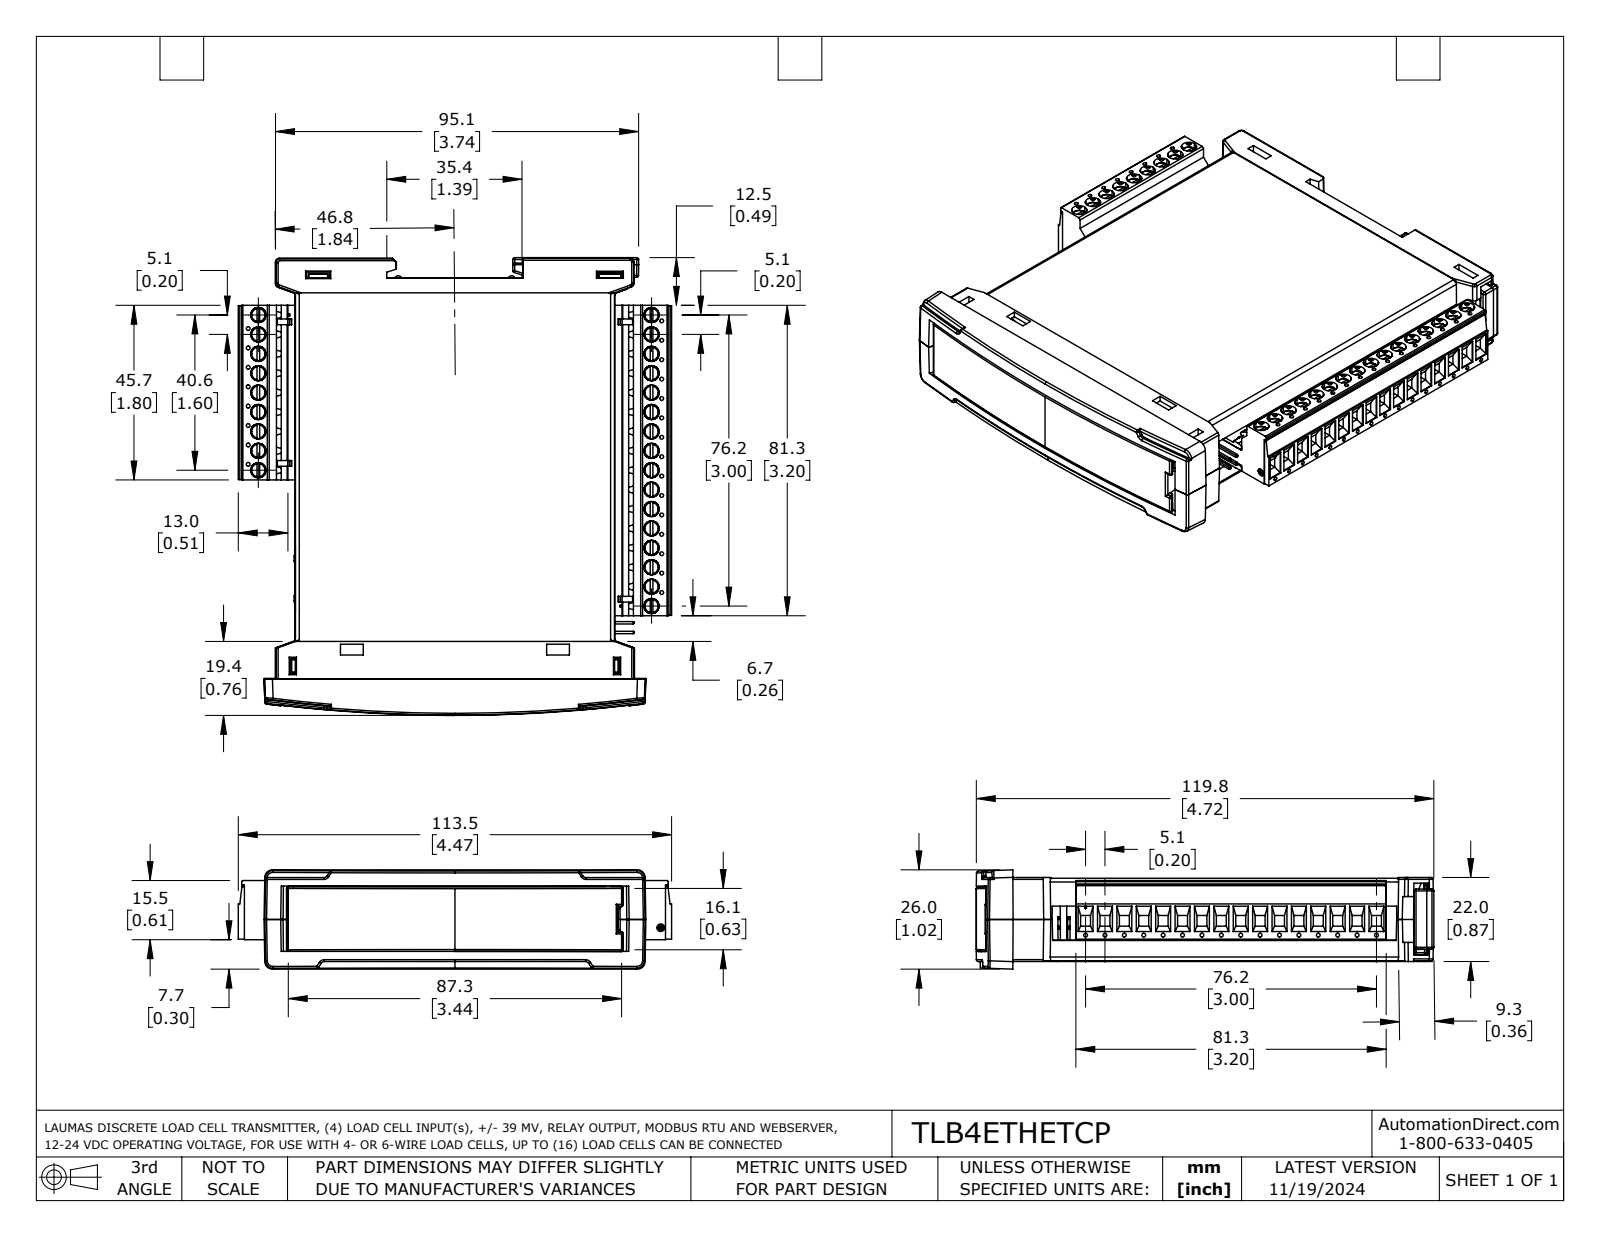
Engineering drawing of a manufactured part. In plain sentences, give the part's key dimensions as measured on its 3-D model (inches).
The part is named "TLB4ETHETCP". Its 3-D file was written by "SolidWorks 2021 (AUTOMOTIVE_DESIGN)". It is 26 solids with 6312 faces: 4003 planar, 1674 cylindrical and 635 other. Overall it measures 4.719 by 4.469 by 1.023 inches. Its volume is 5.296 cubic inches and its surface area 172.4 square inches. Round holes: 56 of diameter 0.039, 25 of diameter 0.157, 16 of diameter 0.059, 16 of diameter 0.146, 6 of diameter 0.079, 4 of diameter 0.029, 4 of diameter 0.035, 2 of diameter 0.067. Round bosses or shafts: 25 of diameter 0.152, 25 of diameter 0.055, 16 of diameter 0.108, 4 of diameter 0.114, 2 of diameter 0.06, 2 of diameter 0.051, 1 of diameter 0.093. Partial cylindrical surfaces (rounded edges, fillets, slot ends): 157 of radius 0.02, 109 of radius 0.004, 64 of radius 0.005, 33 of radius 0.012, 30 of radius 0.039, 16 of radius 0.069, 16 of radius 0.118, 16 of radius 0.122. The main face-to-face distances are 0.051, 0.799, 0.161, 0.059, 0.587, 0.65, 0.748, 0.063, 0.098, 0.701. The hole center spacings are 0.2, 0.4, 0.8, 0.6, 0.6, 4.06, 4.075, 1.
